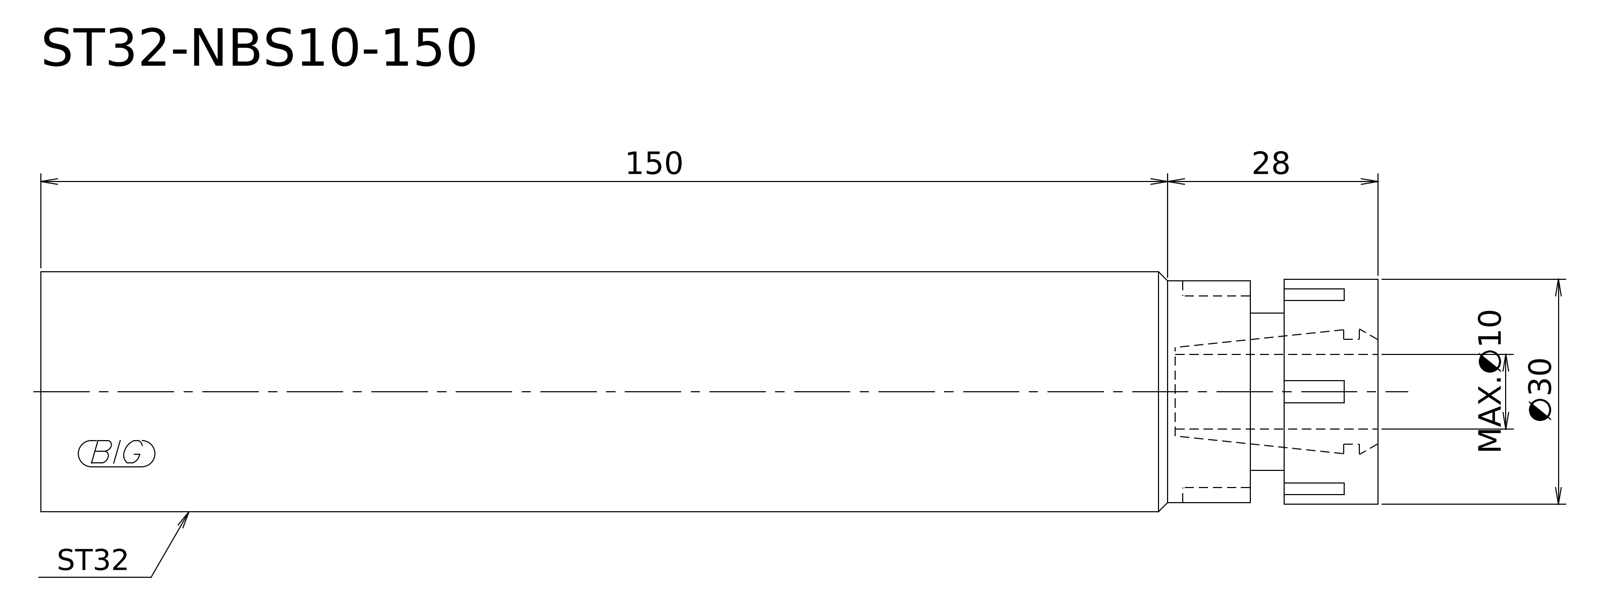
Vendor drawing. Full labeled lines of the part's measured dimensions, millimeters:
STEP written by: Kubotek KeyCreator V8.5.1 (14335) (CONFIG_CONTROL_DESIGN)
Units: millimetres
Bodies: 1 solid, 9 faces (4 planar, 4 cylindrical, 1 other)
Overall size (bounding box): 178 × 32 × 32
Volume: 138 473 mm³ · Surface area: 19 828 mm²
Round bosses / shafts (diameter × count): ⌀32 ×1, ⌀30 ×1, ⌀29.5 ×1, ⌀21 ×1
Main face-to-face distances: 178, 12.5, 165.5, 17, 4.5, 161
